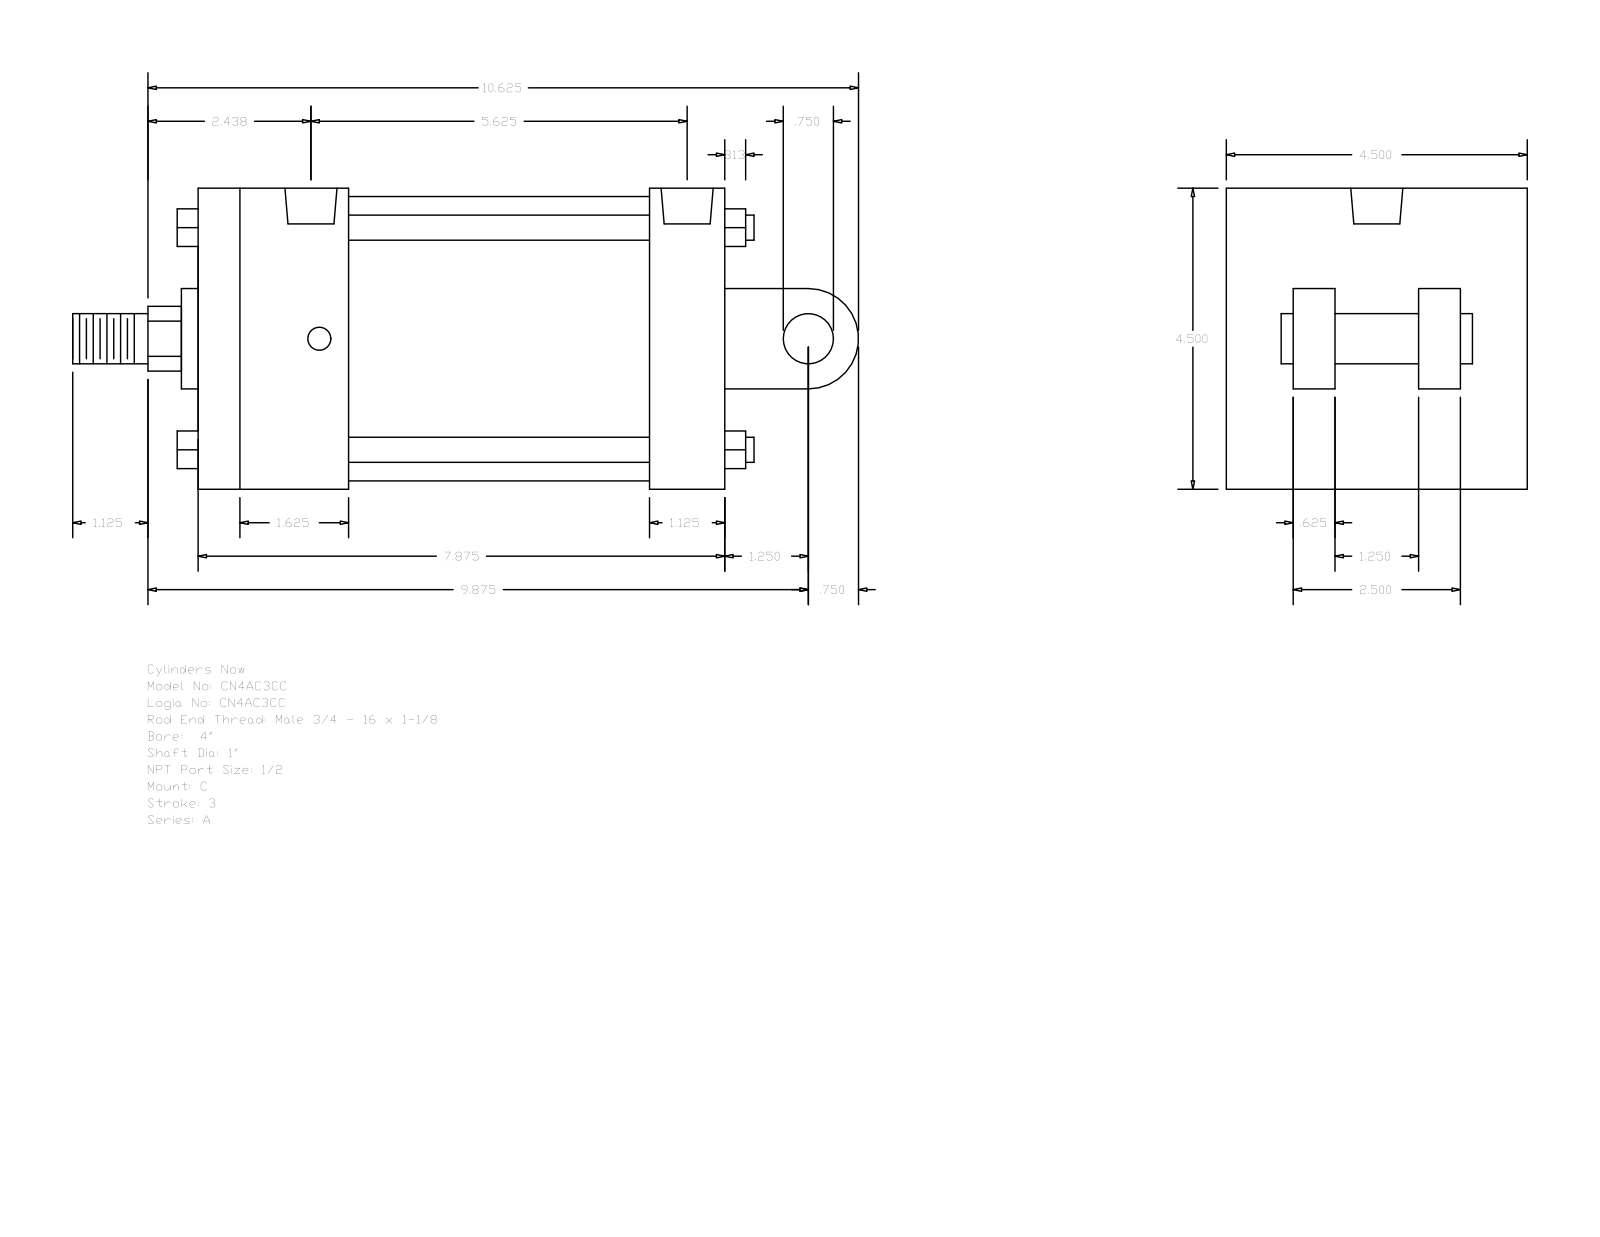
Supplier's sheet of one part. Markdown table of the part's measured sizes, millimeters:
| quantity | value |
| --- | --- |
| part name | A_C__0400_1 |
| STEP written by | GSSL Pune (CONFIG_CONTROL_DESIGN) |
| units | millimeters |
| bodies | 0 solids, 135 faces (102 planar, 33 cylindrical, 0 other) |
| overall size | 298.45 × 114.3 × 114.3 |
| round holes (diameter × count) | 8.73 × 4, 19.77 × 2 |
| round bosses / shafts (diameter × count) | 9.53 × 4, 19.05 × 2, 107.95 × 1, 38.1 × 1, 25.4 × 1 |
| partial cylindrical surfaces (radius × count) | 12.29 × 1, 19.05 × 1 |
| main face-to-face distances | 114.3, 200.02, 73.03, 28.57, 171.45, 57.15, 142.87, 41.27, 38.1, 25.4 |
| hole center spacings | 3.18, 136.52, 139.7, 142.88 |
